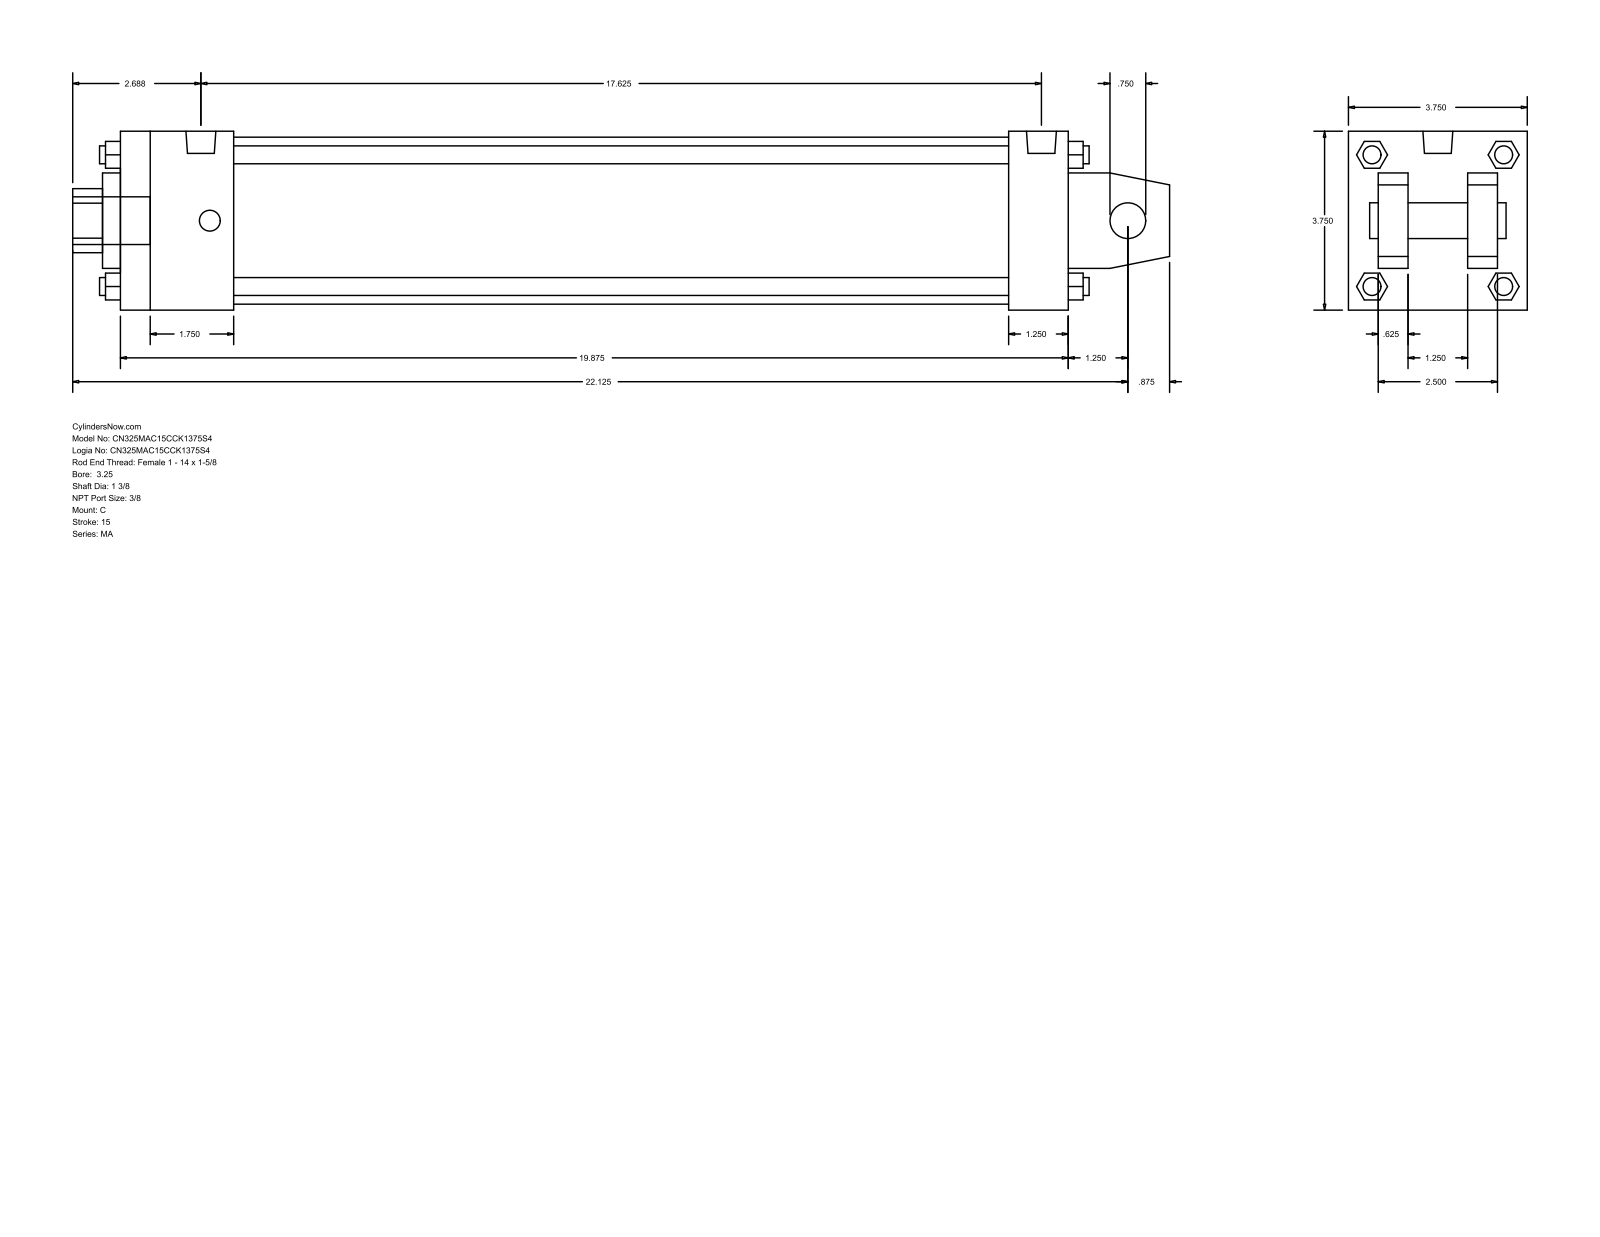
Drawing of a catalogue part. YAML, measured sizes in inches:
part_name: "MA_C__0325_1.375"
step_written_by: "GSSL Pune (CONFIG_CONTROL_DESIGN)"
units: inches
bodies: {solids: 0, faces: 139, planar: 108, cylindrical: 31, other: 0}
overall_size: [23, 3.75, 3.75]
round_holes:
  - {diameter: 0.75, count: 1}
  - {diameter: 1.375, count: 1}
  - {diameter: 2, count: 1}
  - {diameter: 3.5, count: 1}
round_bosses_or_shafts:
  - {diameter: 0.437, count: 4}
  - {diameter: 0.375, count: 4}
  - {diameter: 0.627, count: 2}
  - {diameter: 1, count: 1}
partial_cylinders:
  - {radius: 0.672, count: 1}
face_to_face_distances: [3.75, 0.625, 2.5, 19.875, 1.25, 3.125, 1.875, 18.625, 1.25, 2.375]
